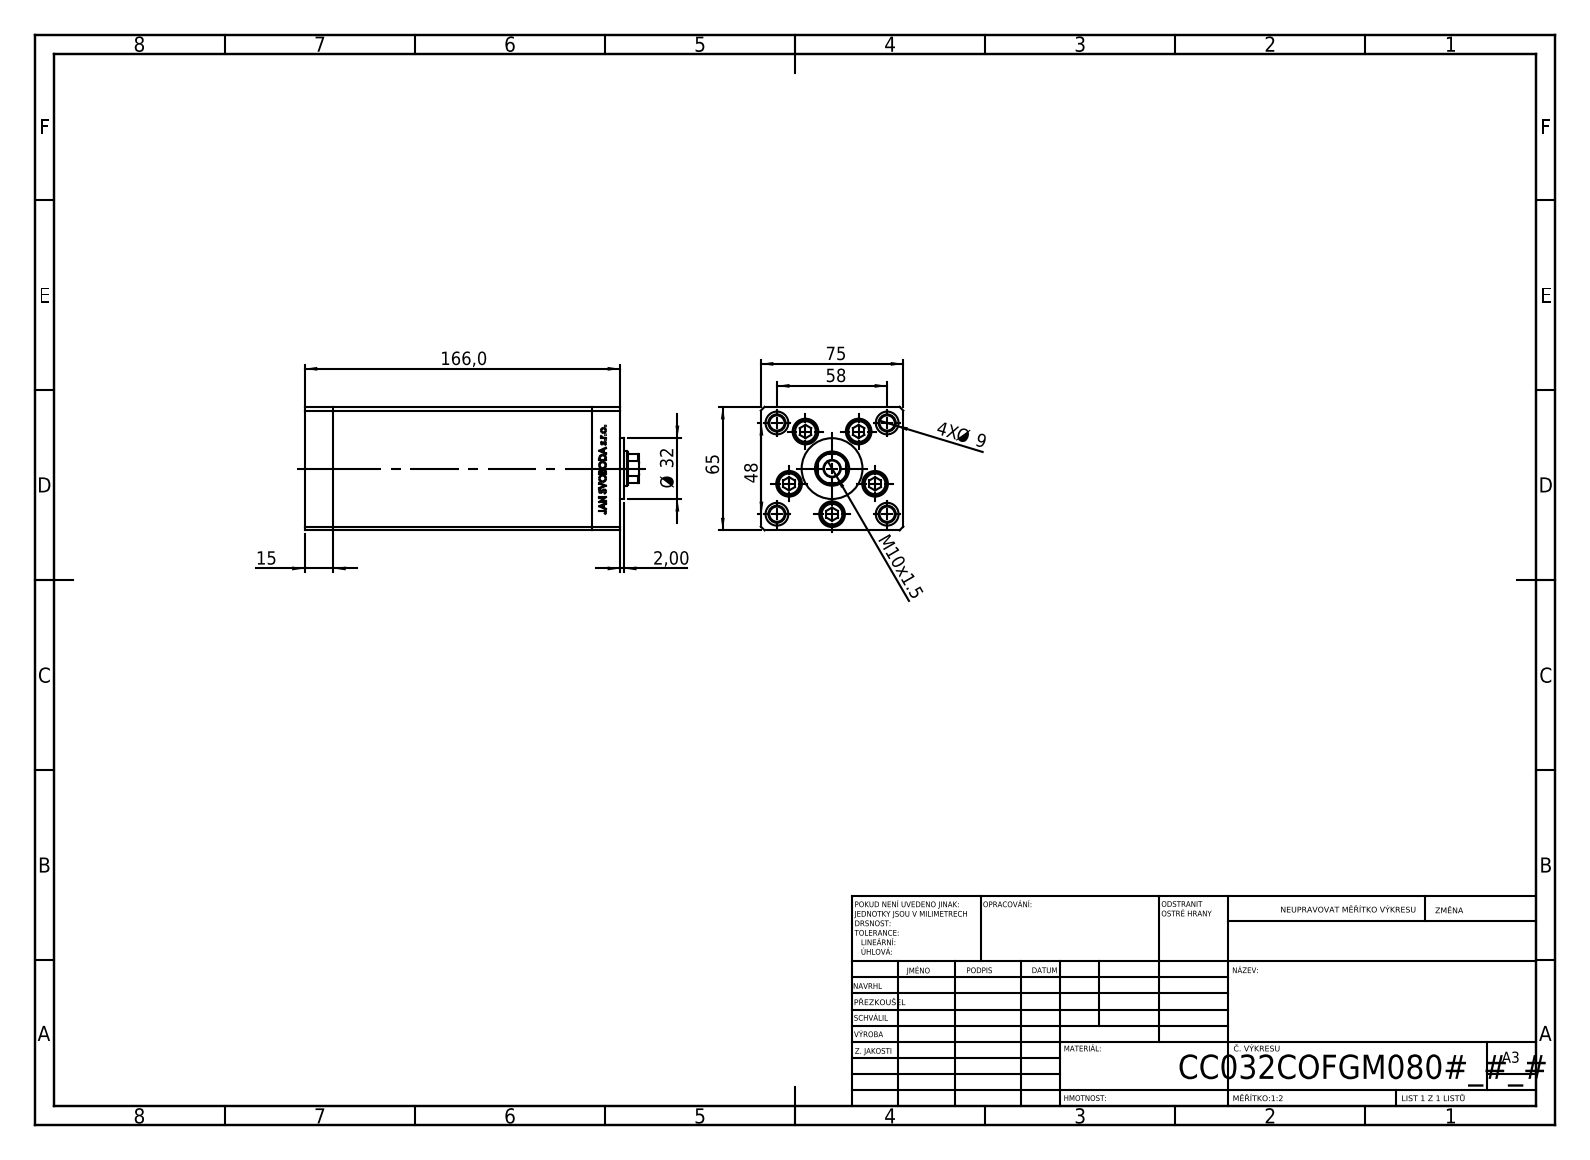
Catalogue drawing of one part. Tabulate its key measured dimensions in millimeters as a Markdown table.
| quantity | value |
| --- | --- |
| part name | ALLEN BOLT; V220C BACK_C; V220C FRONT; V220C_VC_C (+1 more) |
| STEP written by | SolidWorks 2019 (CONFIG_CONTROL_DESIGN) |
| units | millimeters |
| bodies | 13 solids, 1159 faces (538 planar, 159 cylindrical, 462 other) |
| overall size | 176 × 75 × 65 |
| volume | 684 102 mm³ |
| surface area | 141 321 mm² |
| round holes (diameter × count) | 9 × 9, 13.5 × 5, 8 × 4, 12 × 4, 8.5 × 1, 12.5 × 1, 18 × 1 |
| round bosses / shafts (diameter × count) | 8 × 5, 12.5 × 4, 32 × 1 |
| partial cylindrical surfaces (radius × count) | 0.93 × 2, 8.5 × 1 |
| main face-to-face distances | 75, 65, 15, 136, 151, 166, 28, 142, 9, 54.5 |
| hole center spacings | 24, 37.64, 15.67, 17.22, 27.71, 28.83, 29, 32.63 |
